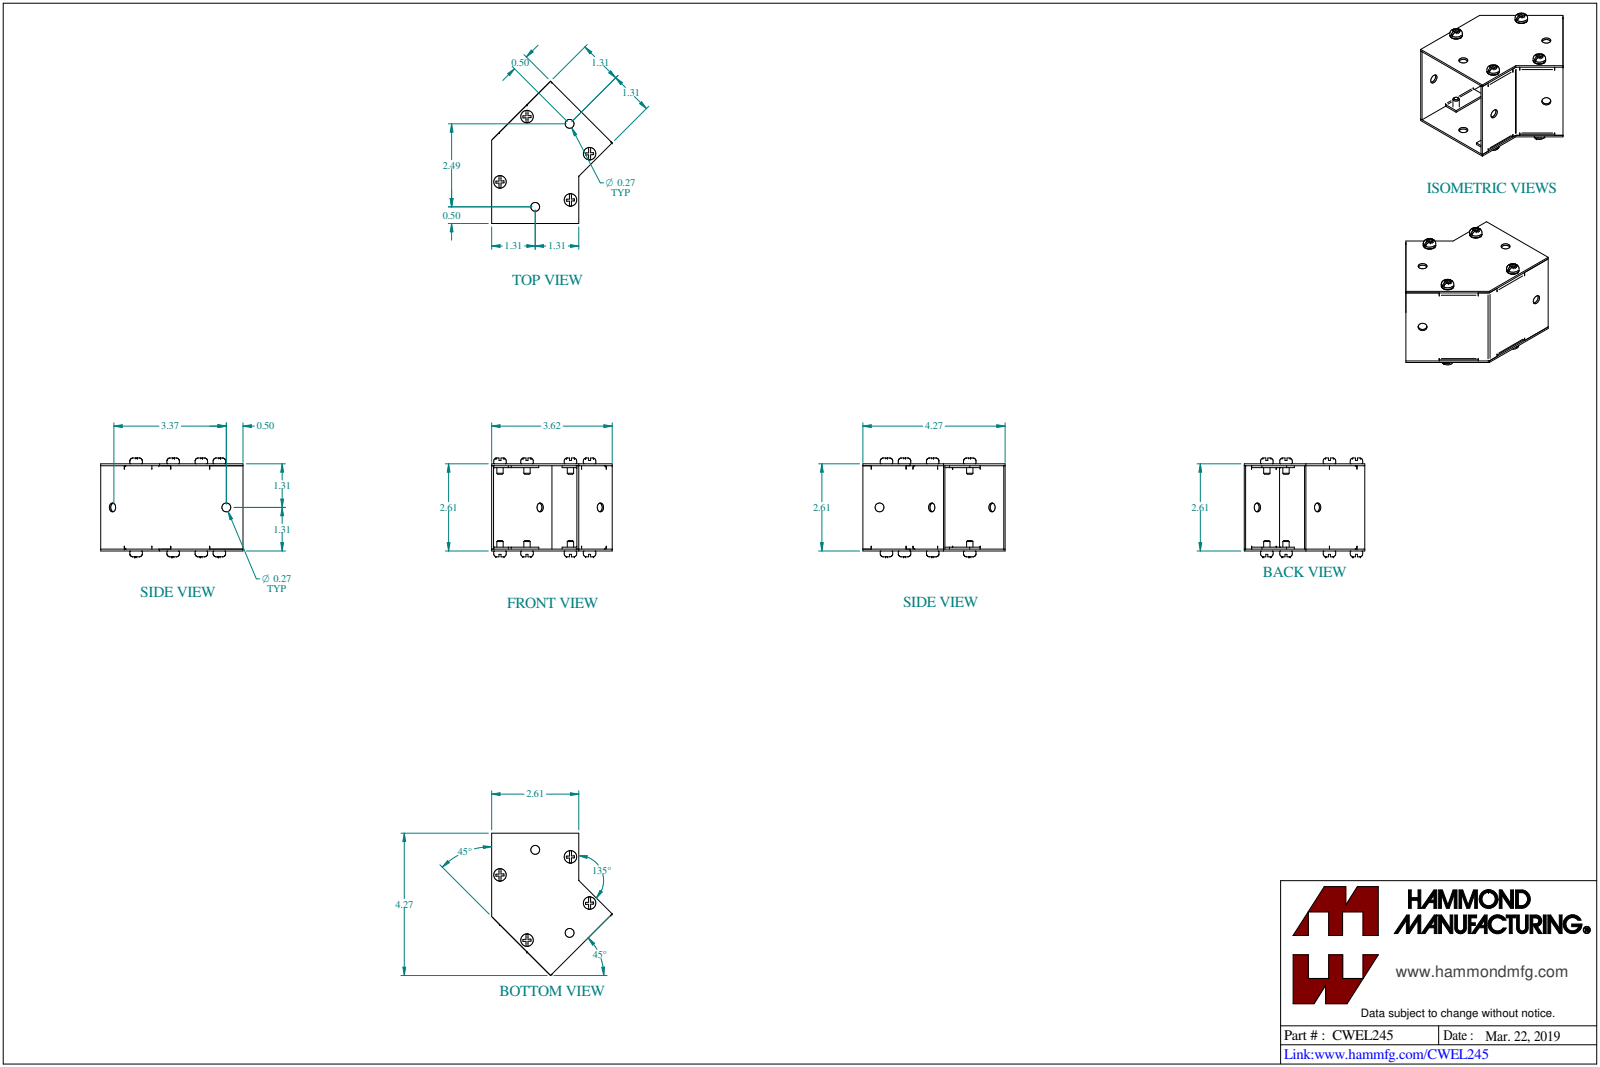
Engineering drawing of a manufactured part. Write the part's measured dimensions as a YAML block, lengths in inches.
part_name: "CWEL245"
step_written_by: "SolidWorks 2023 (CONFIG_CONTROL_DESIGN)"
units: inches
bodies: {solids: 12, faces: 396, planar: 248, cylindrical: 100, other: 48}
overall_size: [4.268, 3.616, 2.964]
volume: 2.626
surface_area: 94.85
round_holes:
  - {diameter: 0.266, count: 5}
  - {diameter: 0.17, count: 4}
  - {diameter: 0.25, count: 4}
round_bosses_or_shafts:
  - {diameter: 0.375, count: 4}
  - {diameter: 0.19, count: 4}
partial_cylinders:
  - {radius: 0.029, count: 10}
  - {radius: 0.086, count: 10}
face_to_face_distances: [0.057, 2.557, 2.5, 2.614, 2.557, 0.114, 2.443, 2.614, 2.5, 2.386]
hole_center_spacings: [1.078, 1.296, 2.182, 2.281, 2.818, 1.077, 1.5, 1.501]
